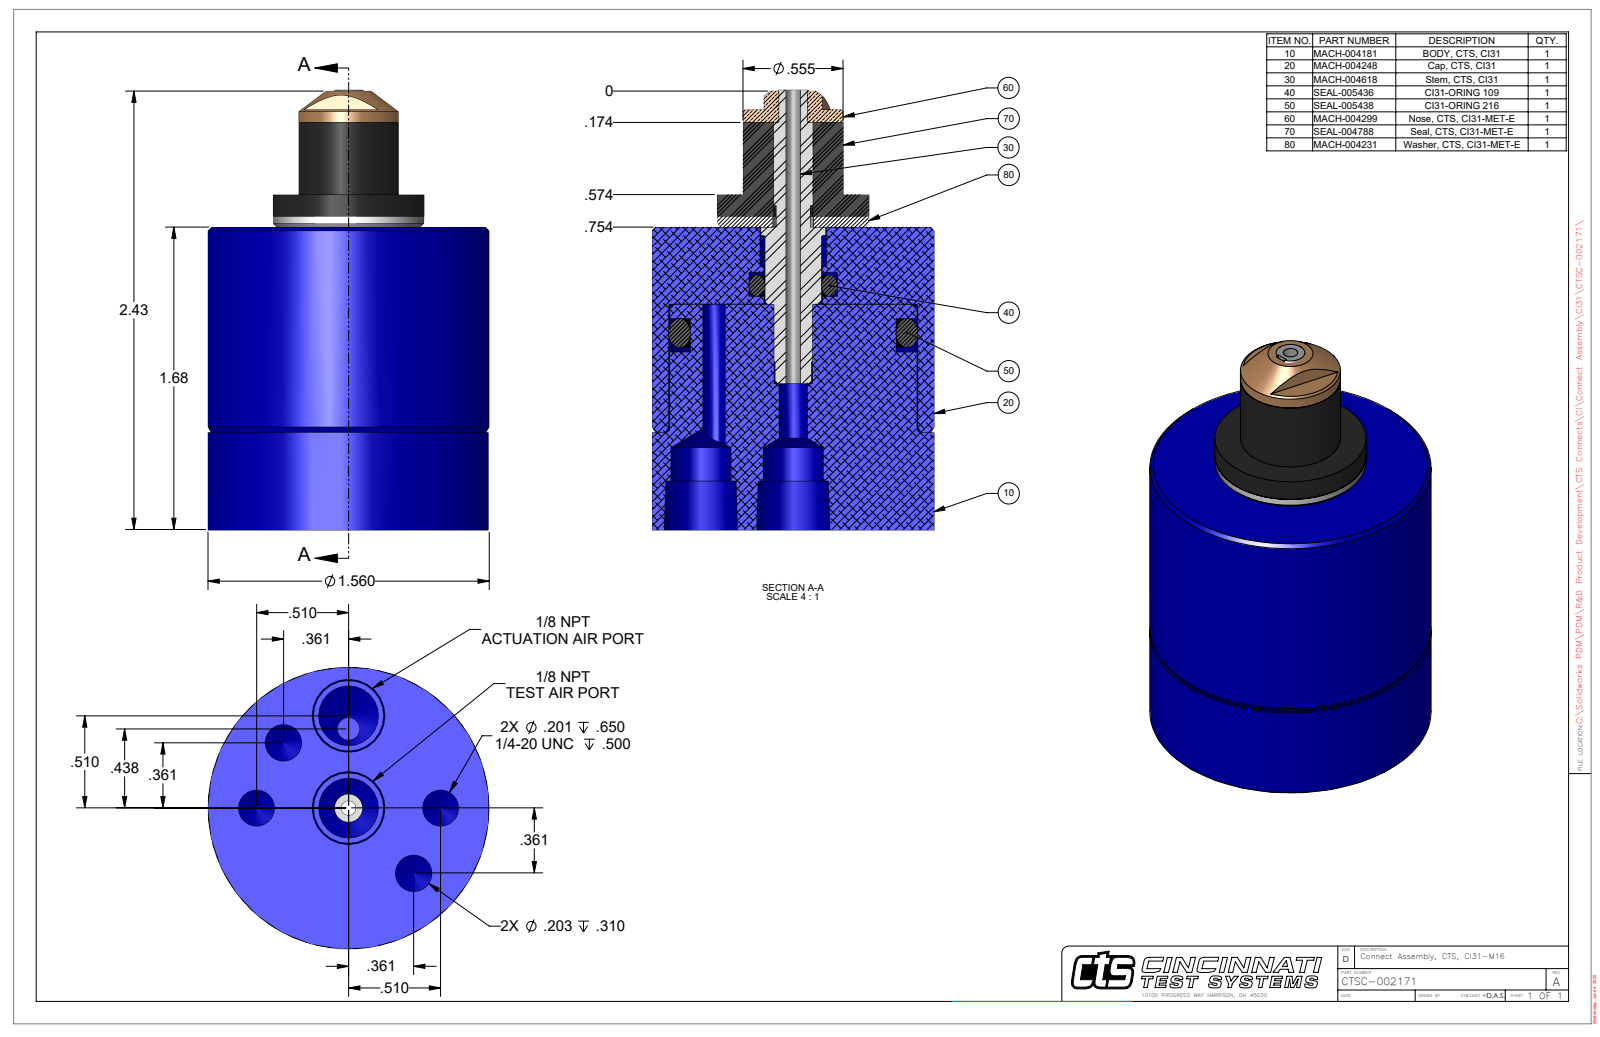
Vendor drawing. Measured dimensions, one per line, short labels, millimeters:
name: CTSC-002171
written by: SolidWorks 2023 (AUTOMOTIVE_DESIGN)
unit: mm
bodies: 1 solid, 90 faces (23 planar, 37 cylindrical, 30 other)
size: 61.9 × 39.6 × 39.6
volume: 52 980 mm³; area: 12 230 mm²
holes: 2× ⌀5.1, 2× ⌀5.2, 2× ⌀8.4, 1× ⌀2.1, 1× ⌀3.2, 1× ⌀4, 1× ⌀9.3, 1× ⌀35
bosses: 1× ⌀39.6, 1× ⌀34.7, 1× ⌀21.3, 1× ⌀21.3, 1× ⌀14.1, 1× ⌀9.1
rounds: 1× R2
face distances: 42.6, 47.2, 4.6, 13.8, 28.8, 33.4, 59.1, 45.3, 16.5, 11.9
hole spacings: 13, 9.9, 23.9, 17.1, 18.3, 1.8, 9.4, 11.1
